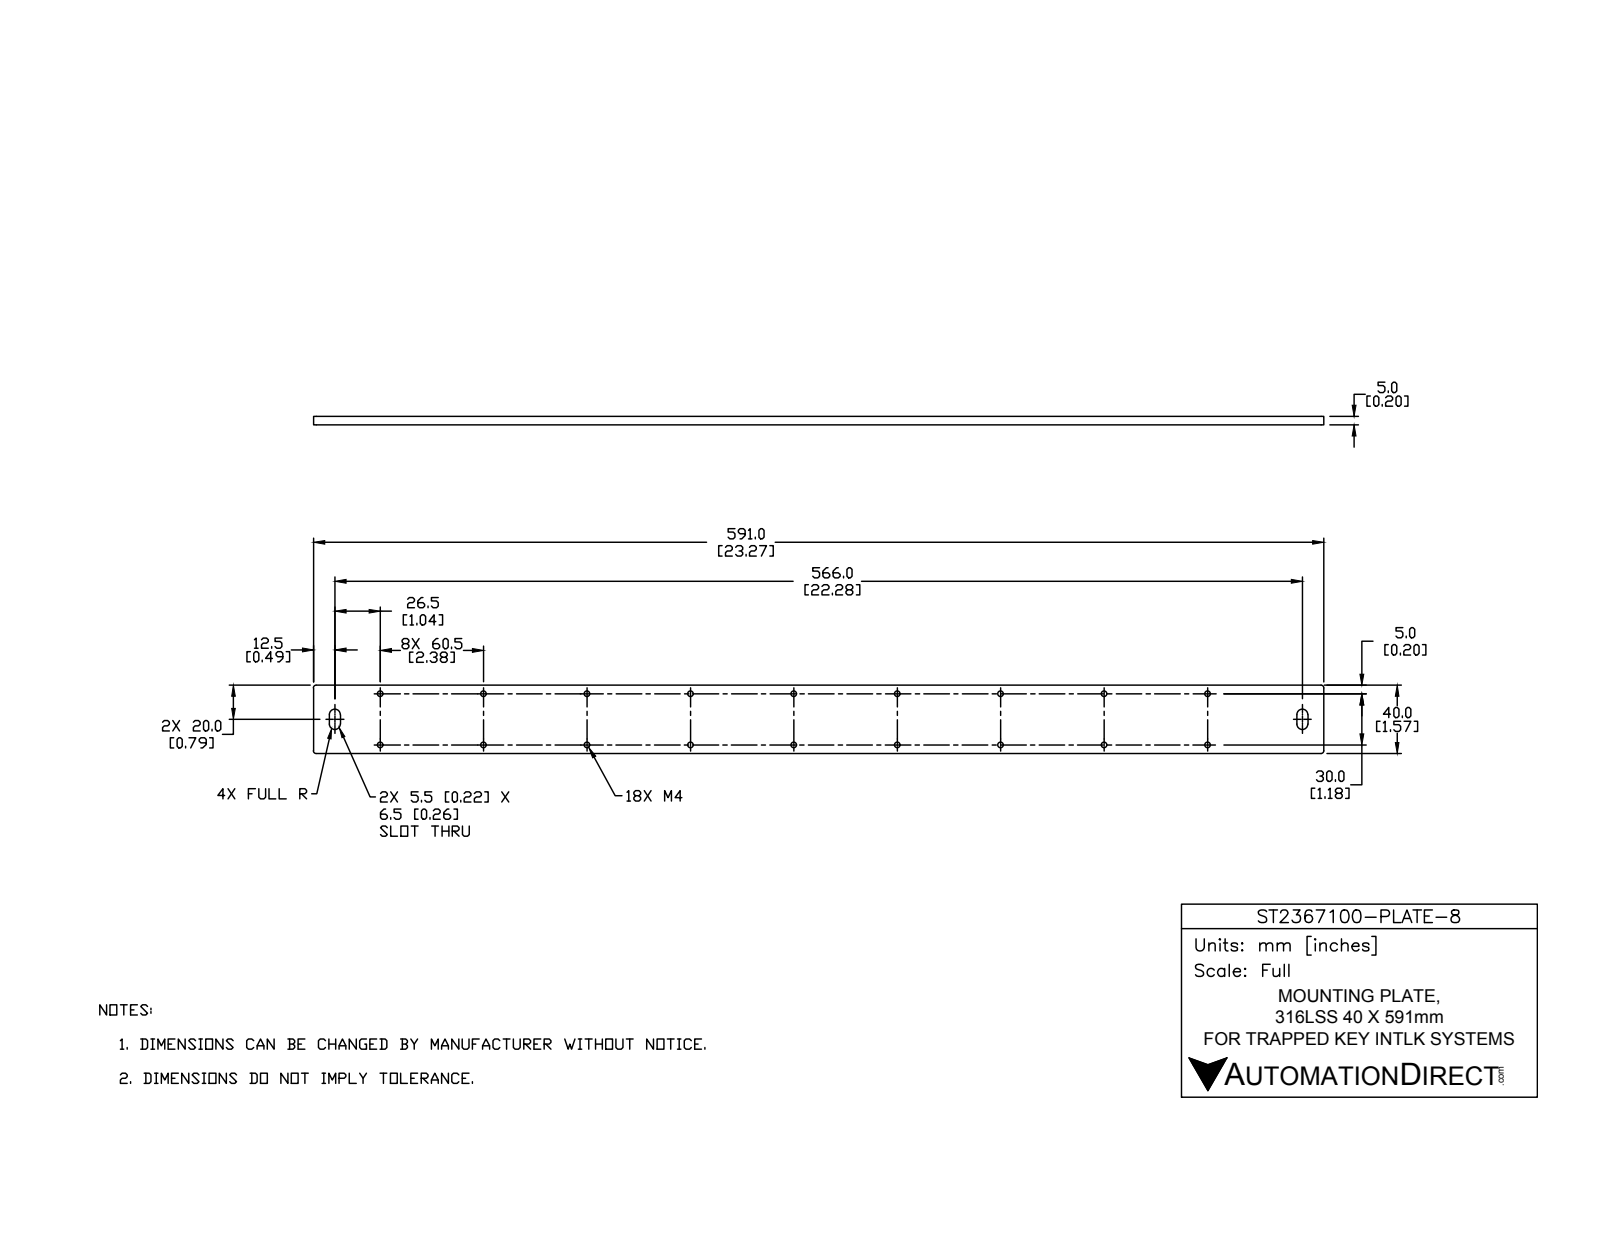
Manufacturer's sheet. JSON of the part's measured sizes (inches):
{"part_name": "ST2367100-PLATE-8", "step_written_by": "SolidWorks 2017 (AUTOMOTIVE_DESIGN)", "units": "inches", "bodies": {"solids": 1, "faces": 68, "planar": 10, "cylindrical": 42, "other": 16}, "overall_size": [23.268, 1.575, 0.197], "volume_in3": 7.116, "surface_area_in2": 83.19, "round_holes": [[0.128, 18]], "partial_cylinders_radius": [[0.008, 8], [0.02, 8], [0.079, 4], [0.128, 4]], "face_to_face_distances": [0.197, 1.575, 23.268, 0.364, 0.62, 22.648, 22.904, 0.256, 22.283, 22.539], "hole_center_spacings": [2.362, 2.641, 4.724, 4.87, 7.087, 7.184, 9.449, 9.522]}
